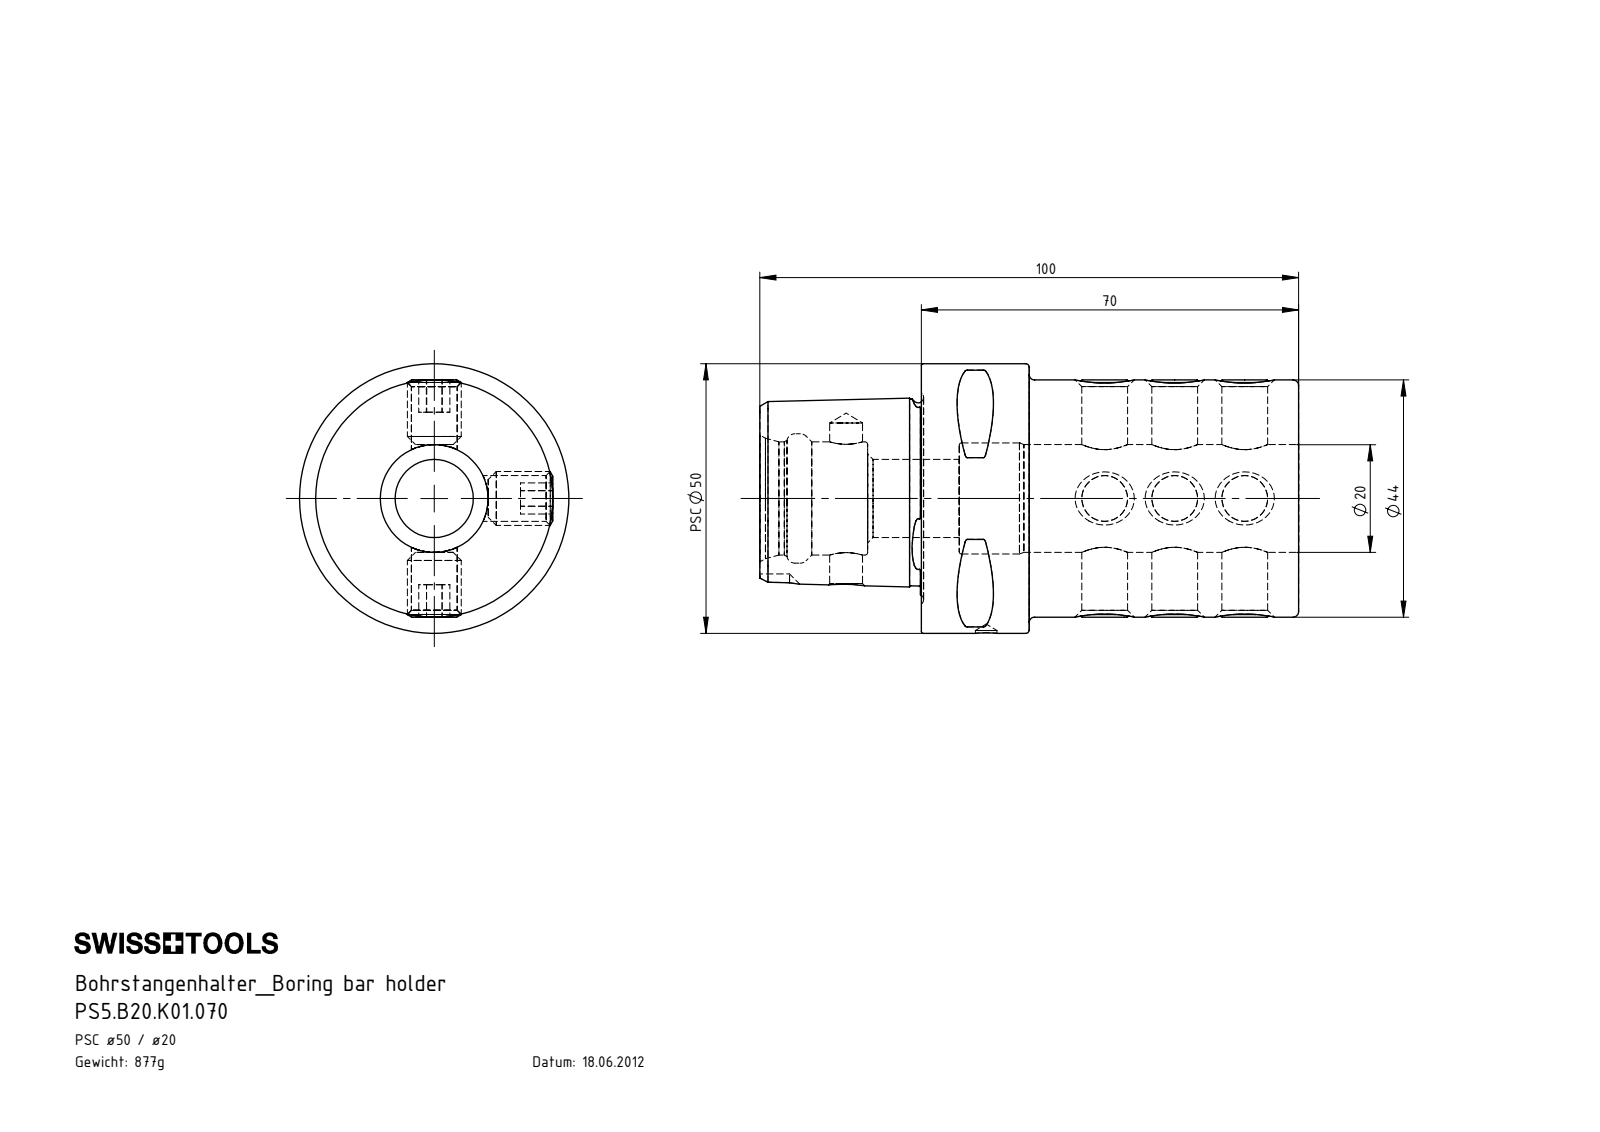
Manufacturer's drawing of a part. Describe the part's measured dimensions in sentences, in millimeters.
The part is named "PS5.B20.K01.070; ISO 4026 - M10 x 12_PreviewCfg; PS5-B20.K01.070_A". Its 3-D file was written by "SolidWorks 2017 (AUTOMOTIVE_DESIGN)". It is 10 solids with 322 faces: 102 planar, 67 cylindrical and 153 other. Overall it measures 100 by 50 by 50 millimeters. Its volume is 111 627 cubic millimeters and its surface area 30 096 square millimeters. Round holes: 6 of diameter 8.5, 1 of diameter 4, 1 of diameter 6.1, 1 of diameter 14.5, 1 of diameter 20, 1 of diameter 20.6, 1 of diameter 21, 1 of diameter 24. Round bosses or shafts: 6 of diameter 10, 1 of diameter 50, 1 of diameter 44. Partial cylindrical surfaces (rounded edges, fillets, slot ends): 8 of radius 0.5, 1 of radius 4. The main face-to-face distances are 70, 30, 20, 50, 5, 100, 6, 13, 6.5, 19.18. The hole center spacings are 13, 26, 48, 22, 35, 61, 74.
